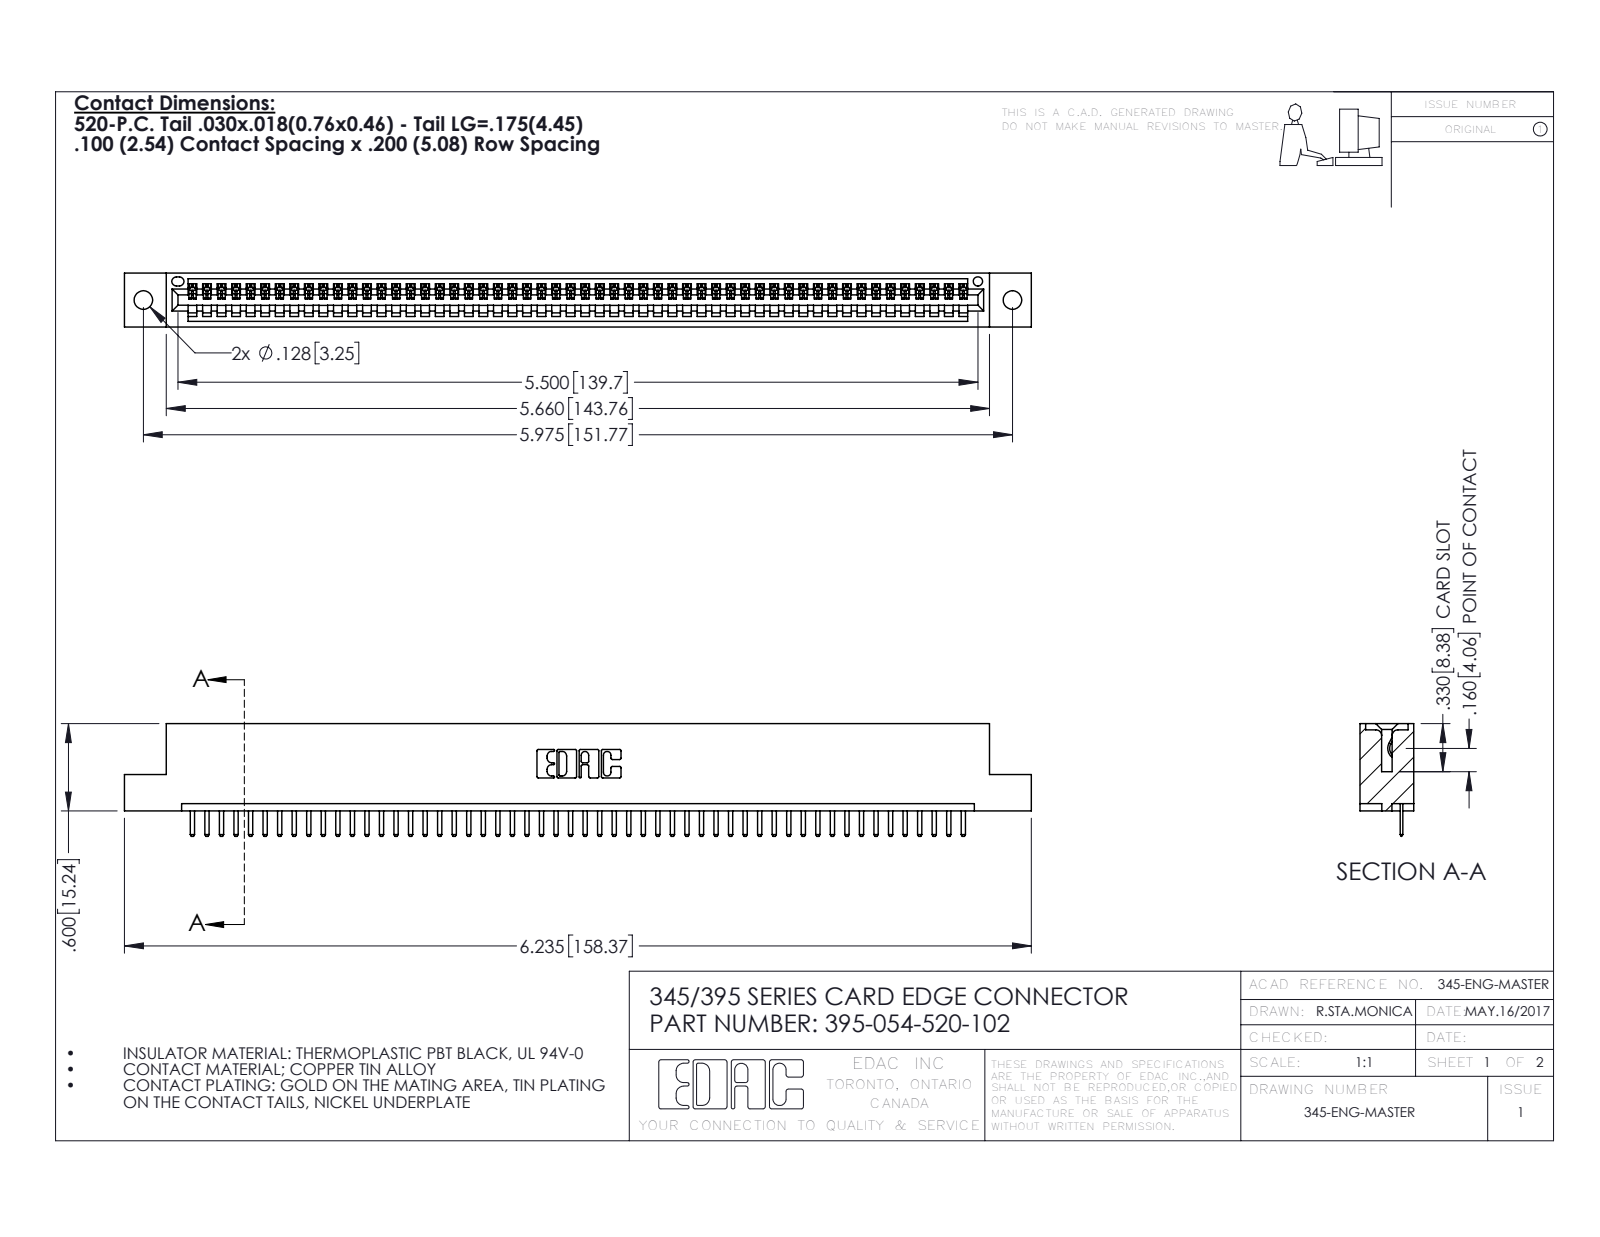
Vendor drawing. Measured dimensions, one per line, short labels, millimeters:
name: 345-292-001_345-293-120; 395-054-520-102; 345 Part_Flush Mounting Lugs - 0.128 Dia
written by: SolidWorks 2016 (CONFIG_CONTROL_DESIGN)
unit: mm
bodies: 55 solids, 3474 faces (2348 planar, 1126 cylindrical, 0 other)
size: 158.4 × 19.7 × 9.4
volume: 14 900 mm³; area: 19 250 mm²
holes: 2× ⌀3.3, 1× ⌀1.6
rounds: 110× R0.3, 108× R0.2, 22× R0.3, 6× R0.2, 6× R0.8, 3× R0.7, 2× R0.8, 2× R1
face distances: 7.6, 1.8, 9.4, 5.1, 2.5, 6.9, 0.6, 5.7, 1.8, 3.8
hole spacings: 6.9, 145.8, 151.8
